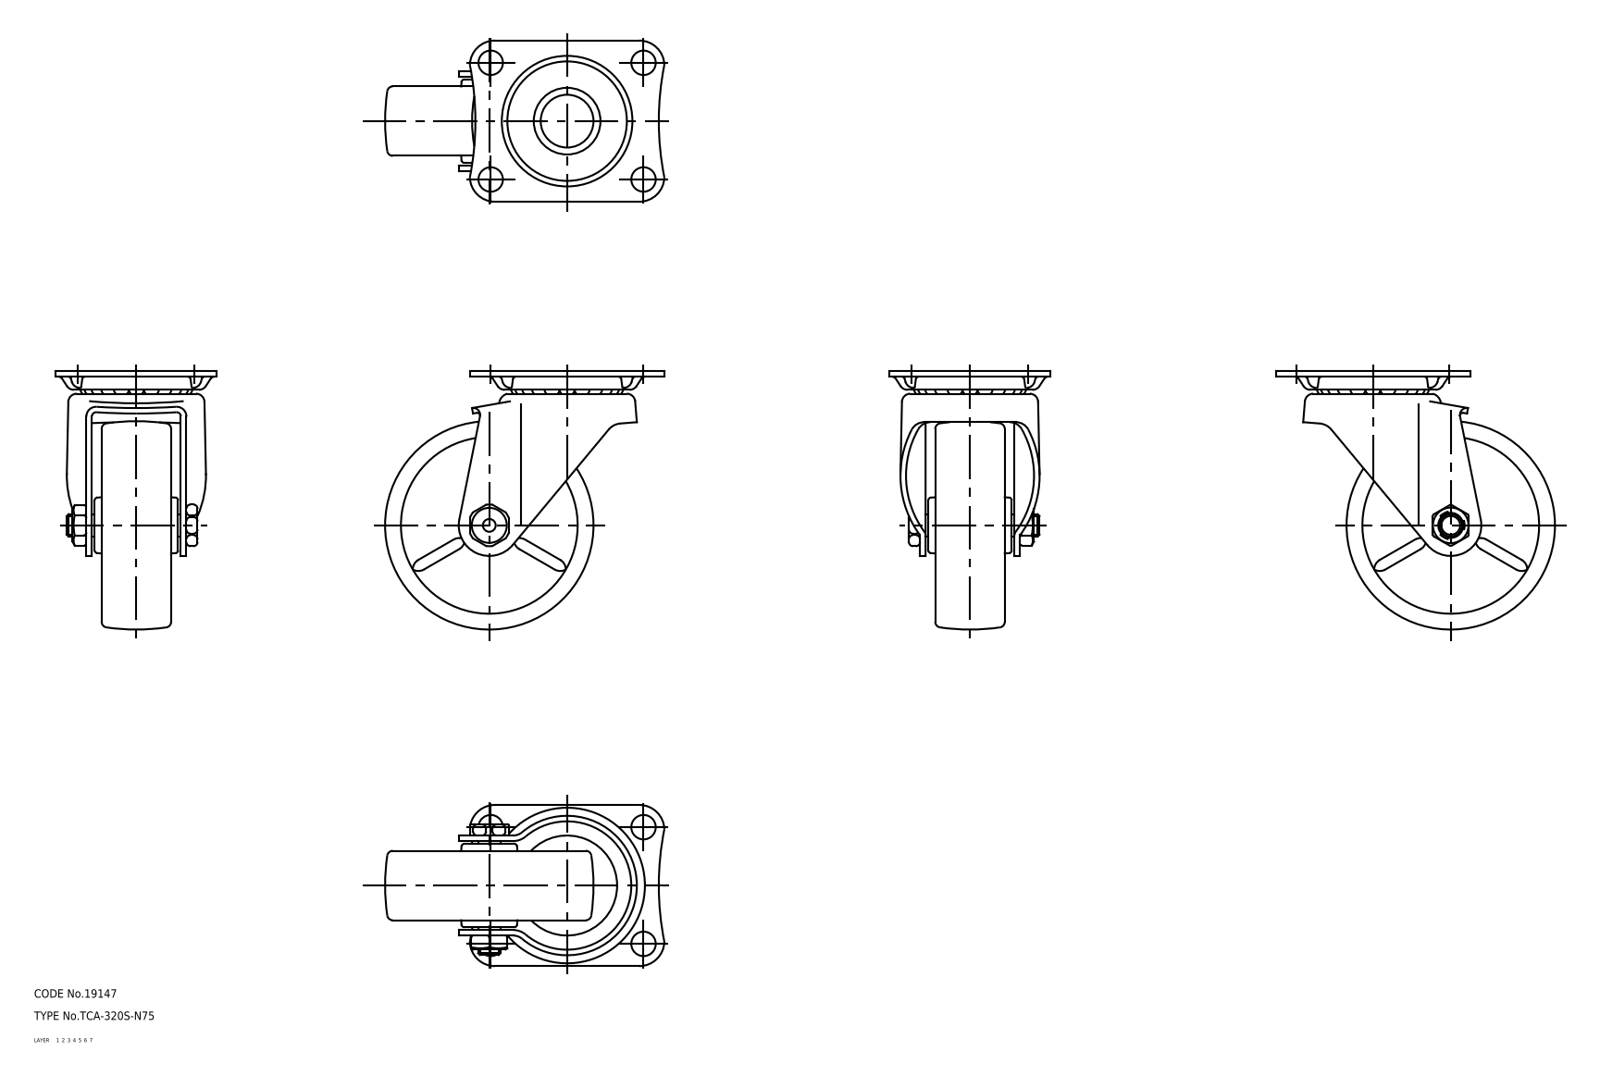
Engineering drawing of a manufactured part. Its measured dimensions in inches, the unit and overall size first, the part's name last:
Units: inches
Overall size (bounding box): 3.957 × 3.661 × 2.283
Volume: 7.078 in³ · Surface area: 72.44 in²
Bodies: 5 solids, 419 faces (0 planar, 0 cylindrical, 419 other)
Part name (STEP PRODUCT): wheel; mounting plate; main shaft; axle (+1 more)
STEP written by: CADfix (AUTOMOTIVE_DESIGN)
